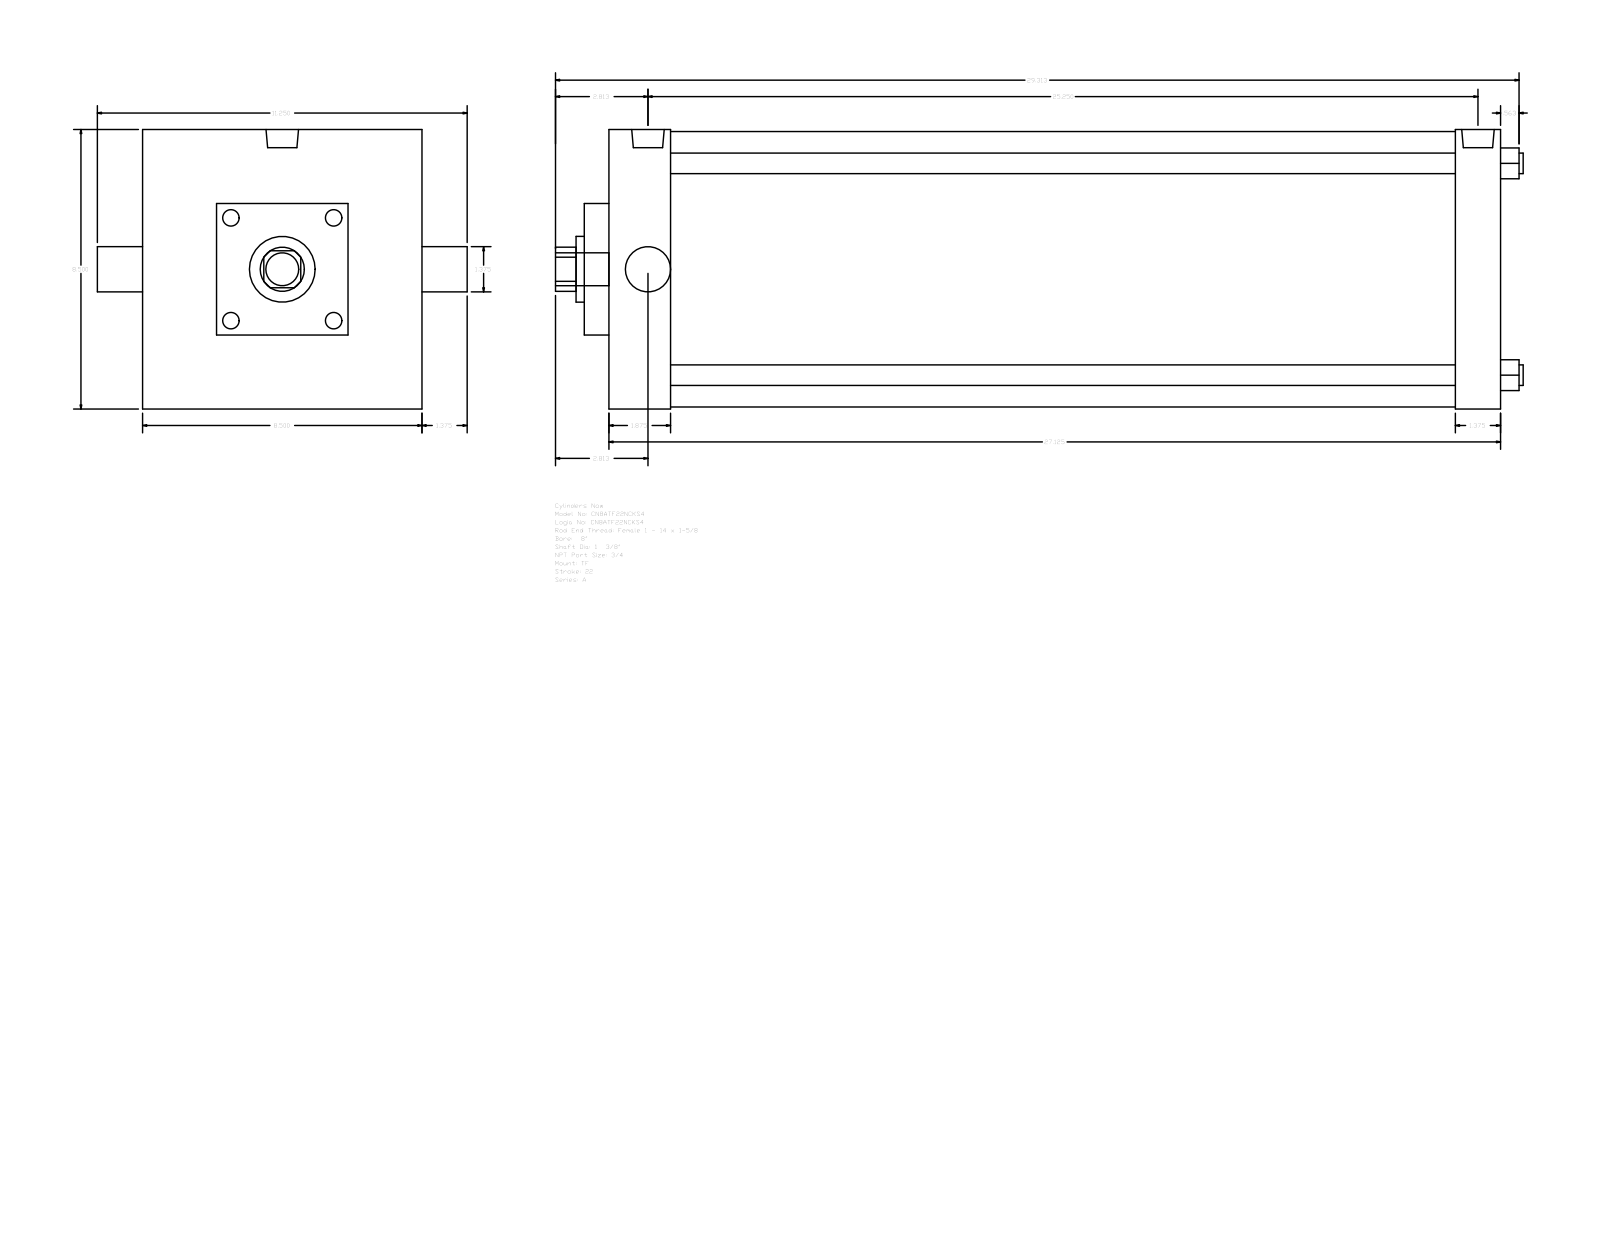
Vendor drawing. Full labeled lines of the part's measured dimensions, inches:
Part name (STEP PRODUCT): A_TF__0800_1.375
STEP written by: GSSL Pune (CONFIG_CONTROL_DESIGN)
Units: inches
Bodies: 0 solids, 89 faces (65 planar, 24 cylindrical, 0 other)
Overall size (bounding box): 29.437 × 11.25 × 8.5
Round holes (diameter × count): ⌀0.625 ×4, ⌀1.375 ×2, ⌀2 ×1, ⌀8.375 ×1
Round bosses / shafts (diameter × count): ⌀0.594 ×3, ⌀0.989 ×2, ⌀1 ×1
Partial cylindrical surfaces — rounded edges, fillets, slot ends (radius × count): R0.672 ×1
Main face-to-face distances: 27.125, 8.5, 1.875, 25.25, 25.75, 23.875, 1.375, 0.75, 2.625, 26.5
Hole centre spacings: 4.554, 6.44, 9.108
